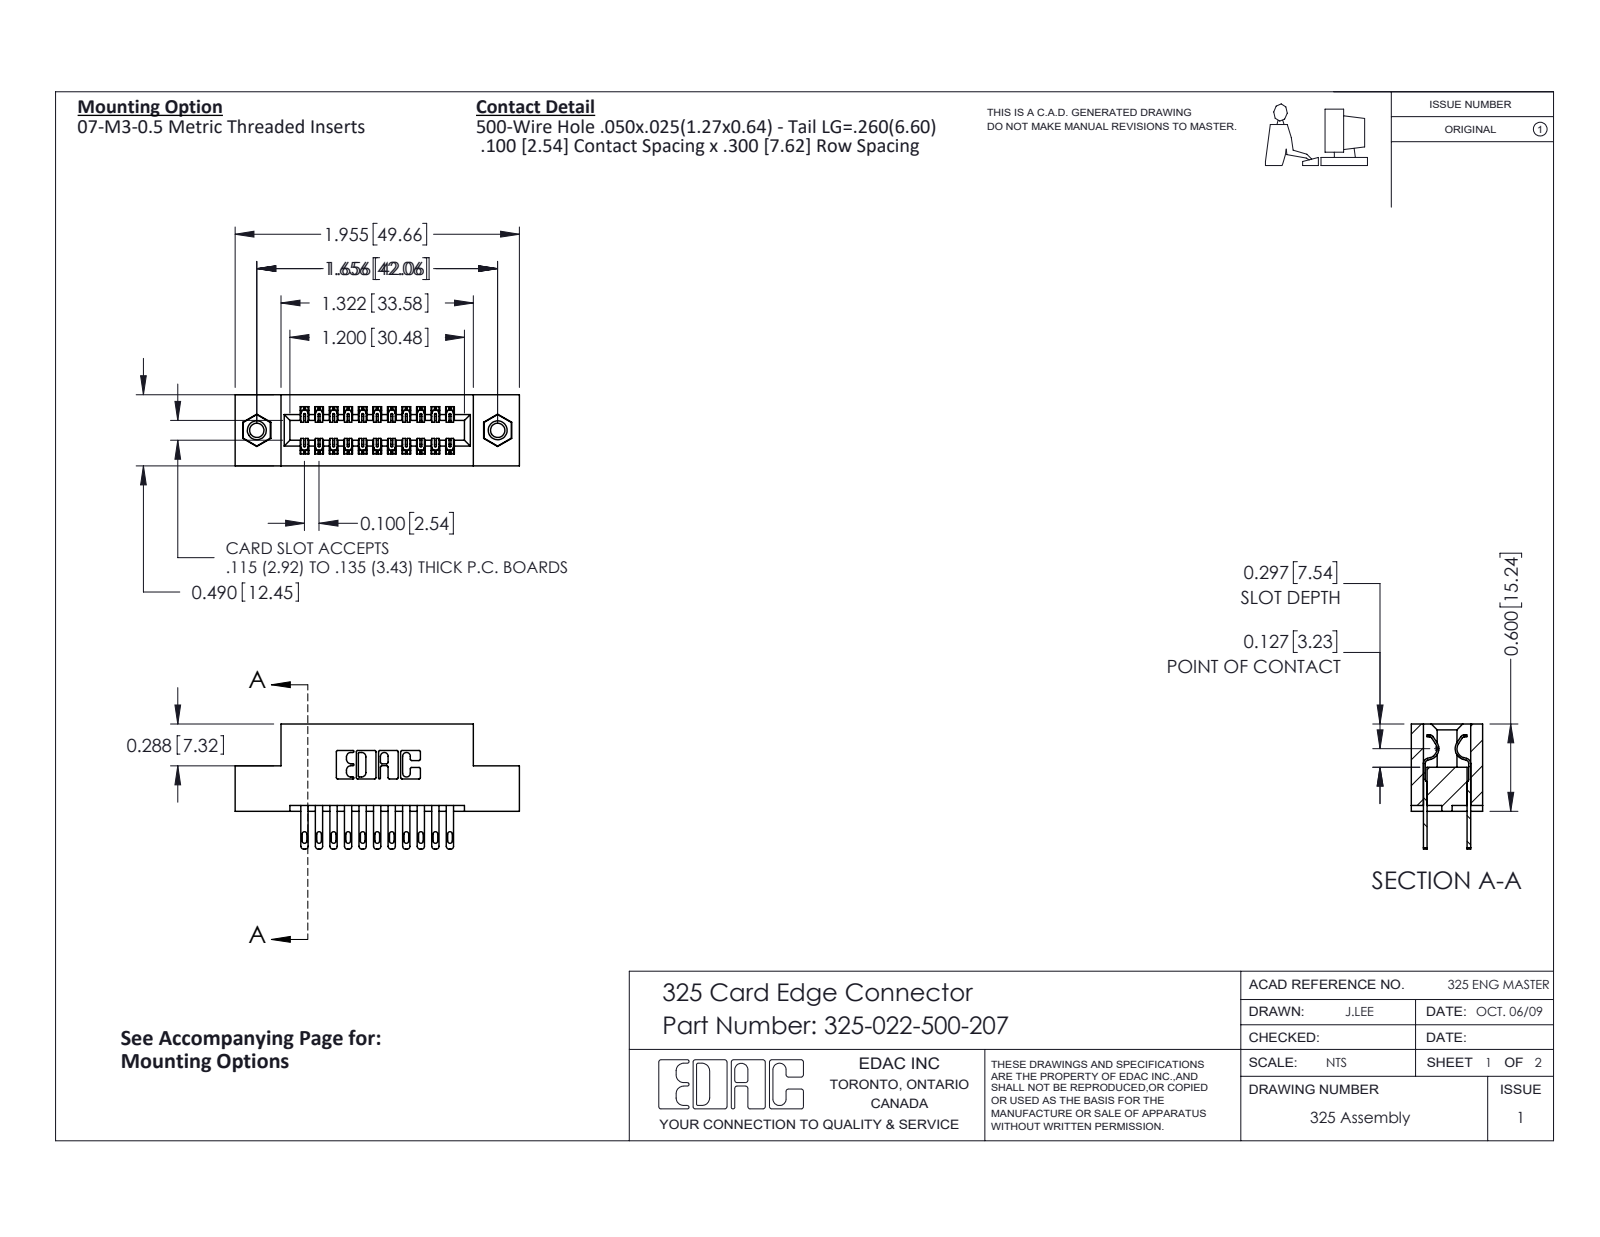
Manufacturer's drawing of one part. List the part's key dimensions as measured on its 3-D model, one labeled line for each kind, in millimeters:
Part name (STEP PRODUCT): 325 Part_TI; 345-250-001_345-250-005-103; 325-292-001_325-293-100; 325-022-500-207
STEP written by: SolidWorks 2016 (CONFIG_CONTROL_DESIGN)
Units: millimetres
Bodies: 25 solids, 1230 faces (762 planar, 452 cylindrical, 16 other)
Overall size (bounding box): 49.7 × 21.8 × 12.4
Volume: 6 180 mm³ · Surface area: 7 006 mm²
Round holes (diameter × count): ⌀2.5 ×2, ⌀3.2 ×2, ⌀4.1 ×2
Round bosses / shafts (diameter × count): ⌀3.9 ×2
Partial cylindrical surfaces — rounded edges, fillets, slot ends (radius × count): R0.2 ×33, R0.3 ×22, R0.4 ×22, R0.5 ×22, R0.2 ×6, R0.8 ×6, R0.7 ×3, R0.4 ×2
Main face-to-face distances: 7.6, 2.1, 10.3, 12.4, 1, 2.7, 9.7, 0.6, 2.5, 5.1
Hole centre spacings: 42.1
